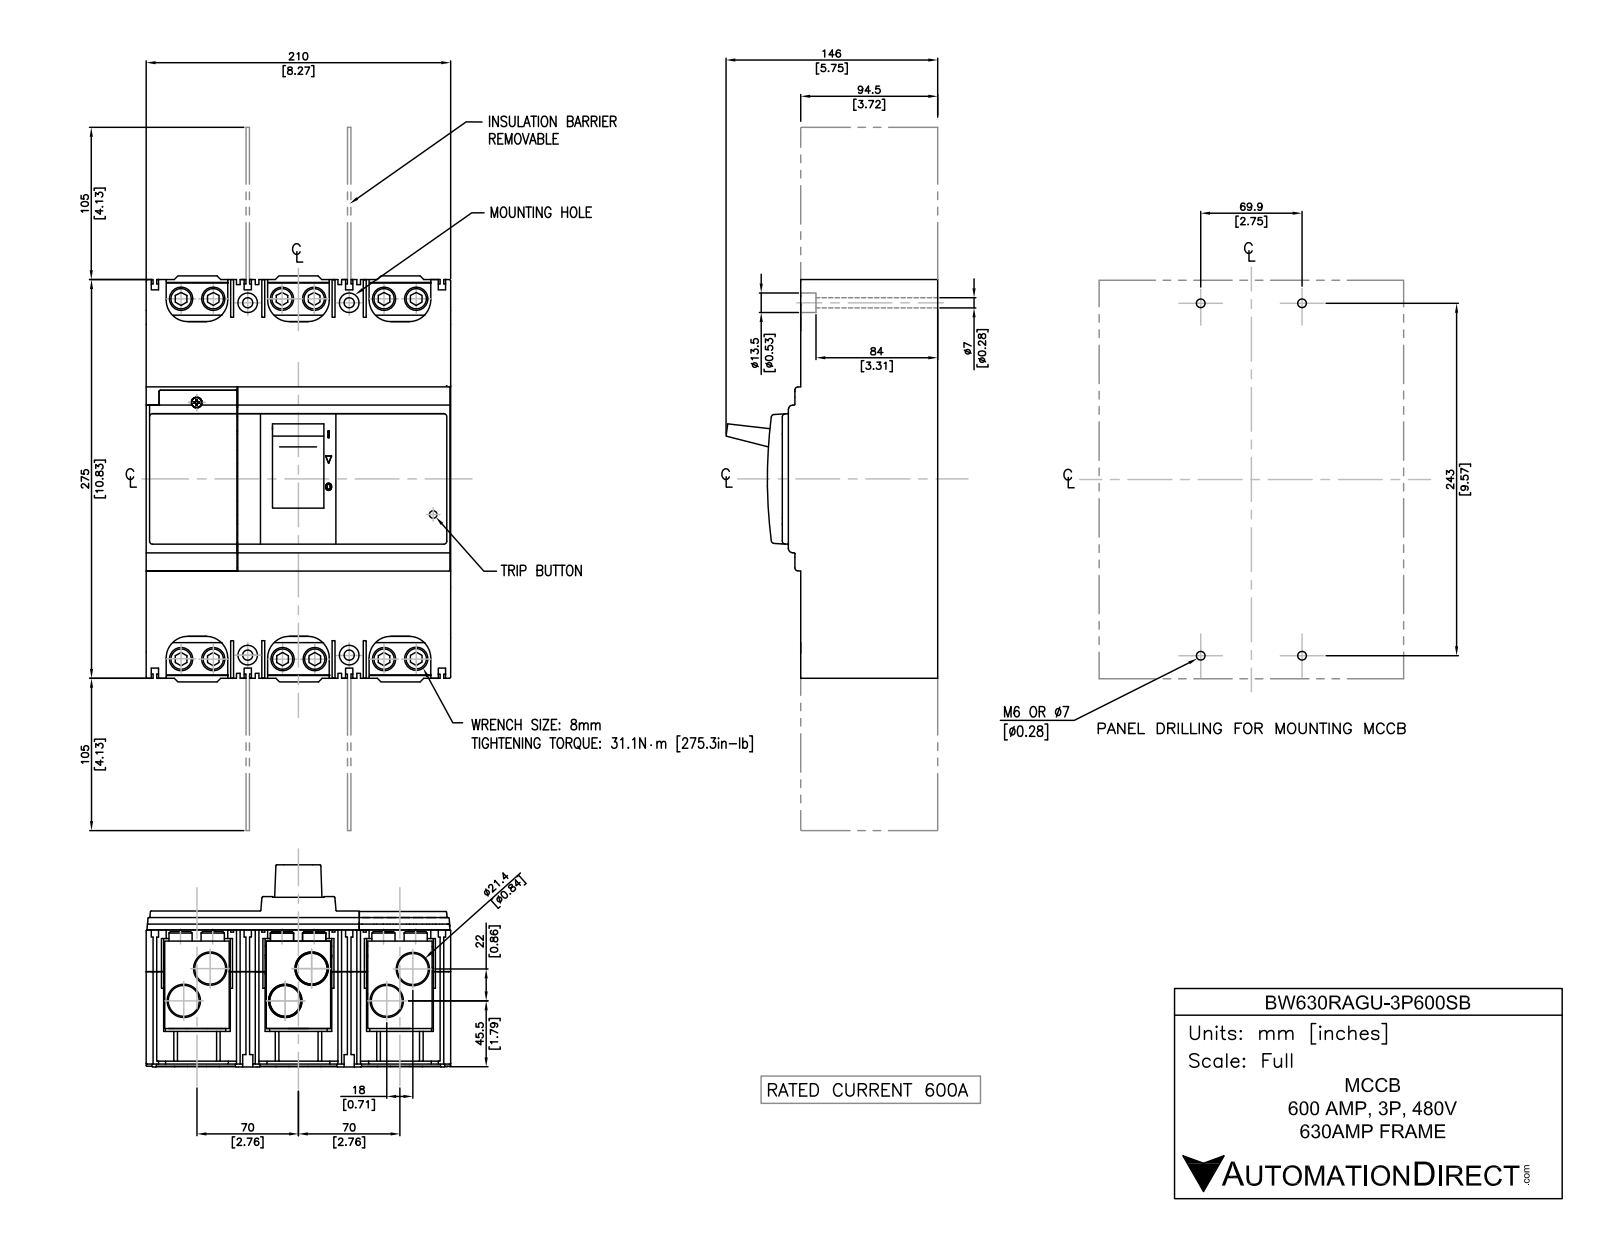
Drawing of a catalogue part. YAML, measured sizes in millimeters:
part_name: "BW630RAGU-3P600SB"
step_written_by: "SolidWorks 2018 (AUTOMOTIVE_DESIGN)"
units: millimeters
bodies: {solids: 44, faces: 975, planar: 505, cylindrical: 314, other: 156}
overall_size: [275, 210, 143.2]
volume: 5416000
surface_area: 387300
round_holes:
  - {diameter: 6.1, count: 12}
  - {diameter: 7.1, count: 12}
  - {diameter: 14.3, count: 12}
  - {diameter: 16, count: 12}
  - {diameter: 12, count: 6}
  - {diameter: 21.4, count: 6}
  - {diameter: 3.5, count: 4}
  - {diameter: 7, count: 4}
  - {diameter: 13.5, count: 4}
  - {diameter: 5.2, count: 1}
round_bosses_or_shafts:
  - {diameter: 16, count: 12}
  - {diameter: 12.2, count: 12}
  - {diameter: 10.5, count: 12}
  - {diameter: 6, count: 12}
partial_cylinders:
  - {radius: 0.7, count: 48}
  - {radius: 15, count: 12}
face_to_face_distances: [210, 94.5, 70, 12.5, 107, 44.2, 22.2, 4, 2.4, 24.6]
hole_center_spacings: [70, 11.4, 245.7, 24, 35, 46.2, 59, 81.1]
